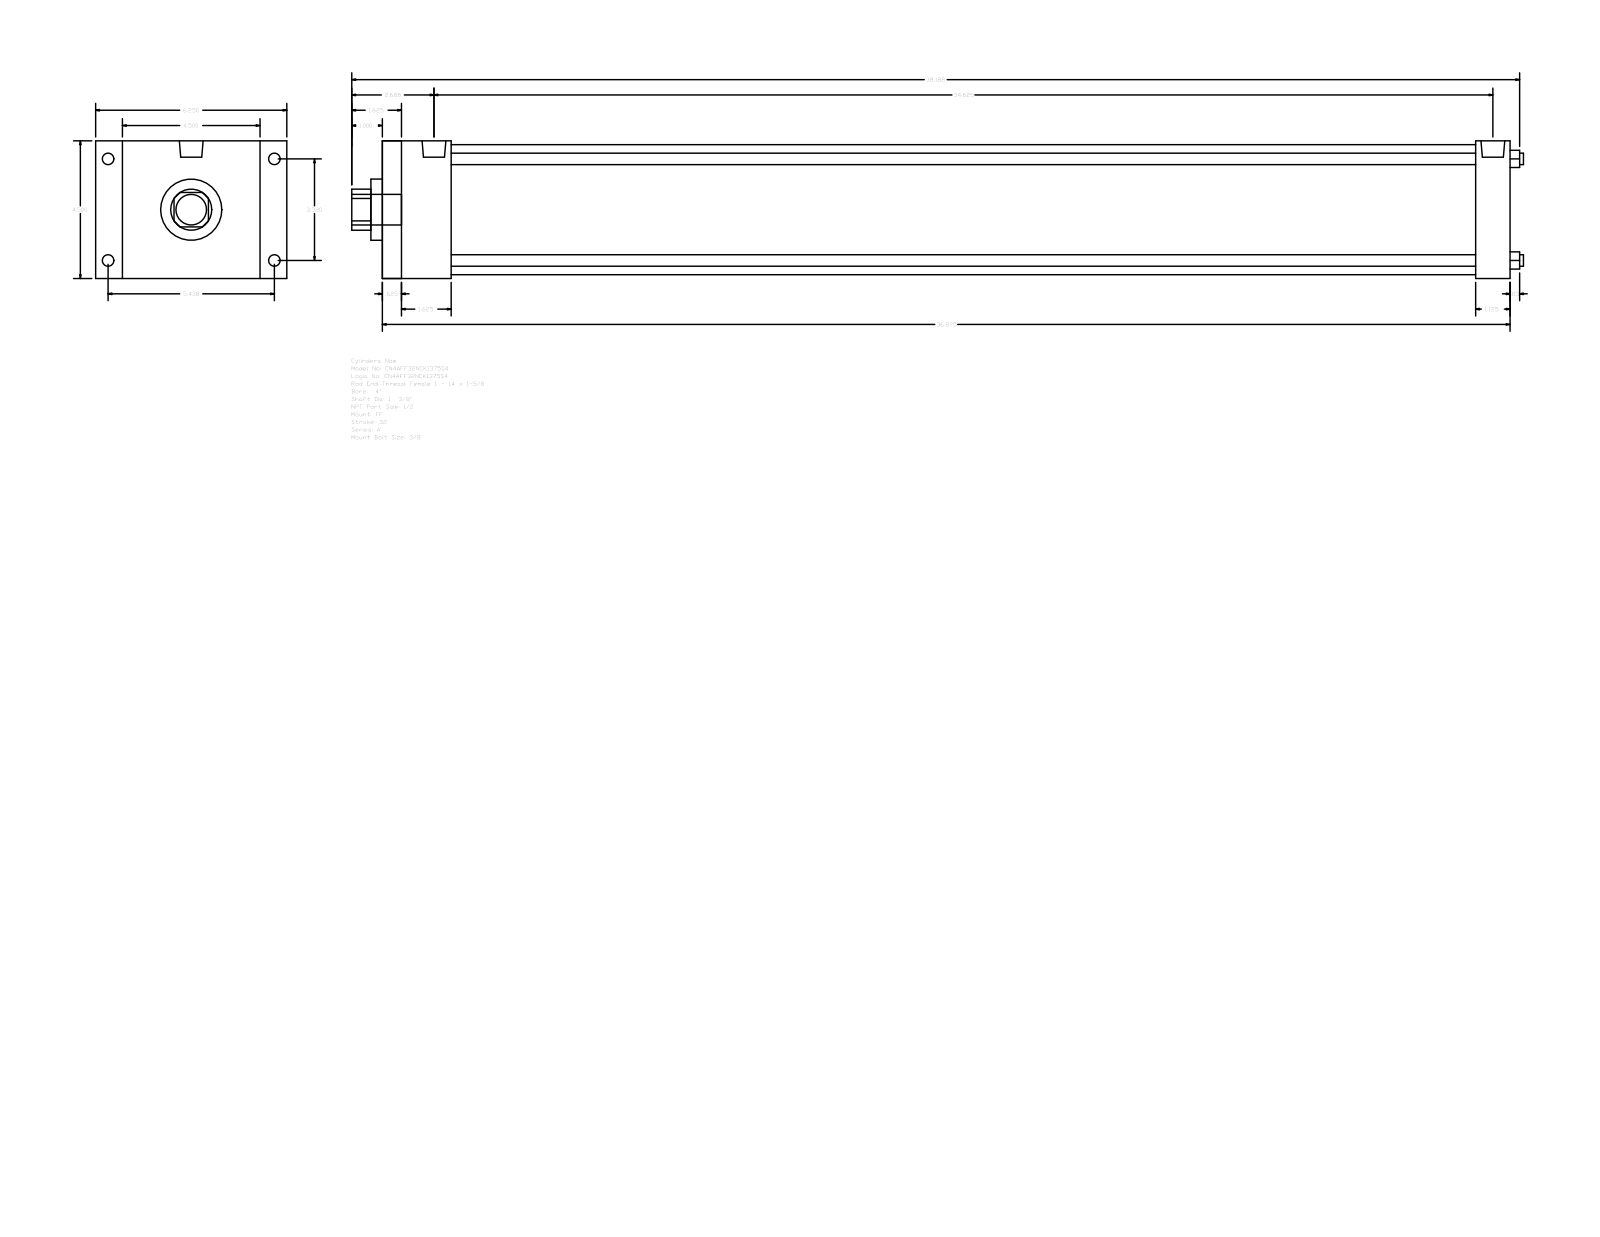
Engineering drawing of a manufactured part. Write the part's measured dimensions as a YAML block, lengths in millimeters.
part_name: "A_FF__0400_1.375"
step_written_by: "GSSL Pune (CONFIG_CONTROL_DESIGN)"
units: millimeters
bodies: {solids: 0, faces: 92, planar: 64, cylindrical: 28, other: 0}
overall_size: [973.14, 158.75, 114.3]
round_holes:
  - {diameter: 9.53, count: 4}
  - {diameter: 34.92, count: 1}
  - {diameter: 50.8, count: 1}
  - {diameter: 107.95, count: 1}
round_bosses_or_shafts:
  - {diameter: 9.53, count: 4}
  - {diameter: 8.73, count: 4}
  - {diameter: 19.77, count: 2}
  - {diameter: 25.4, count: 1}
partial_cylinders:
  - {radius: 17.06, count: 1}
face_to_face_distances: [114.3, 936.62, 920.75, 15.87, 28.57, 22.23, 136.53, 908.05, 892.18, 57.15]
hole_center_spacings: [59.62, 84.32, 119.25]
